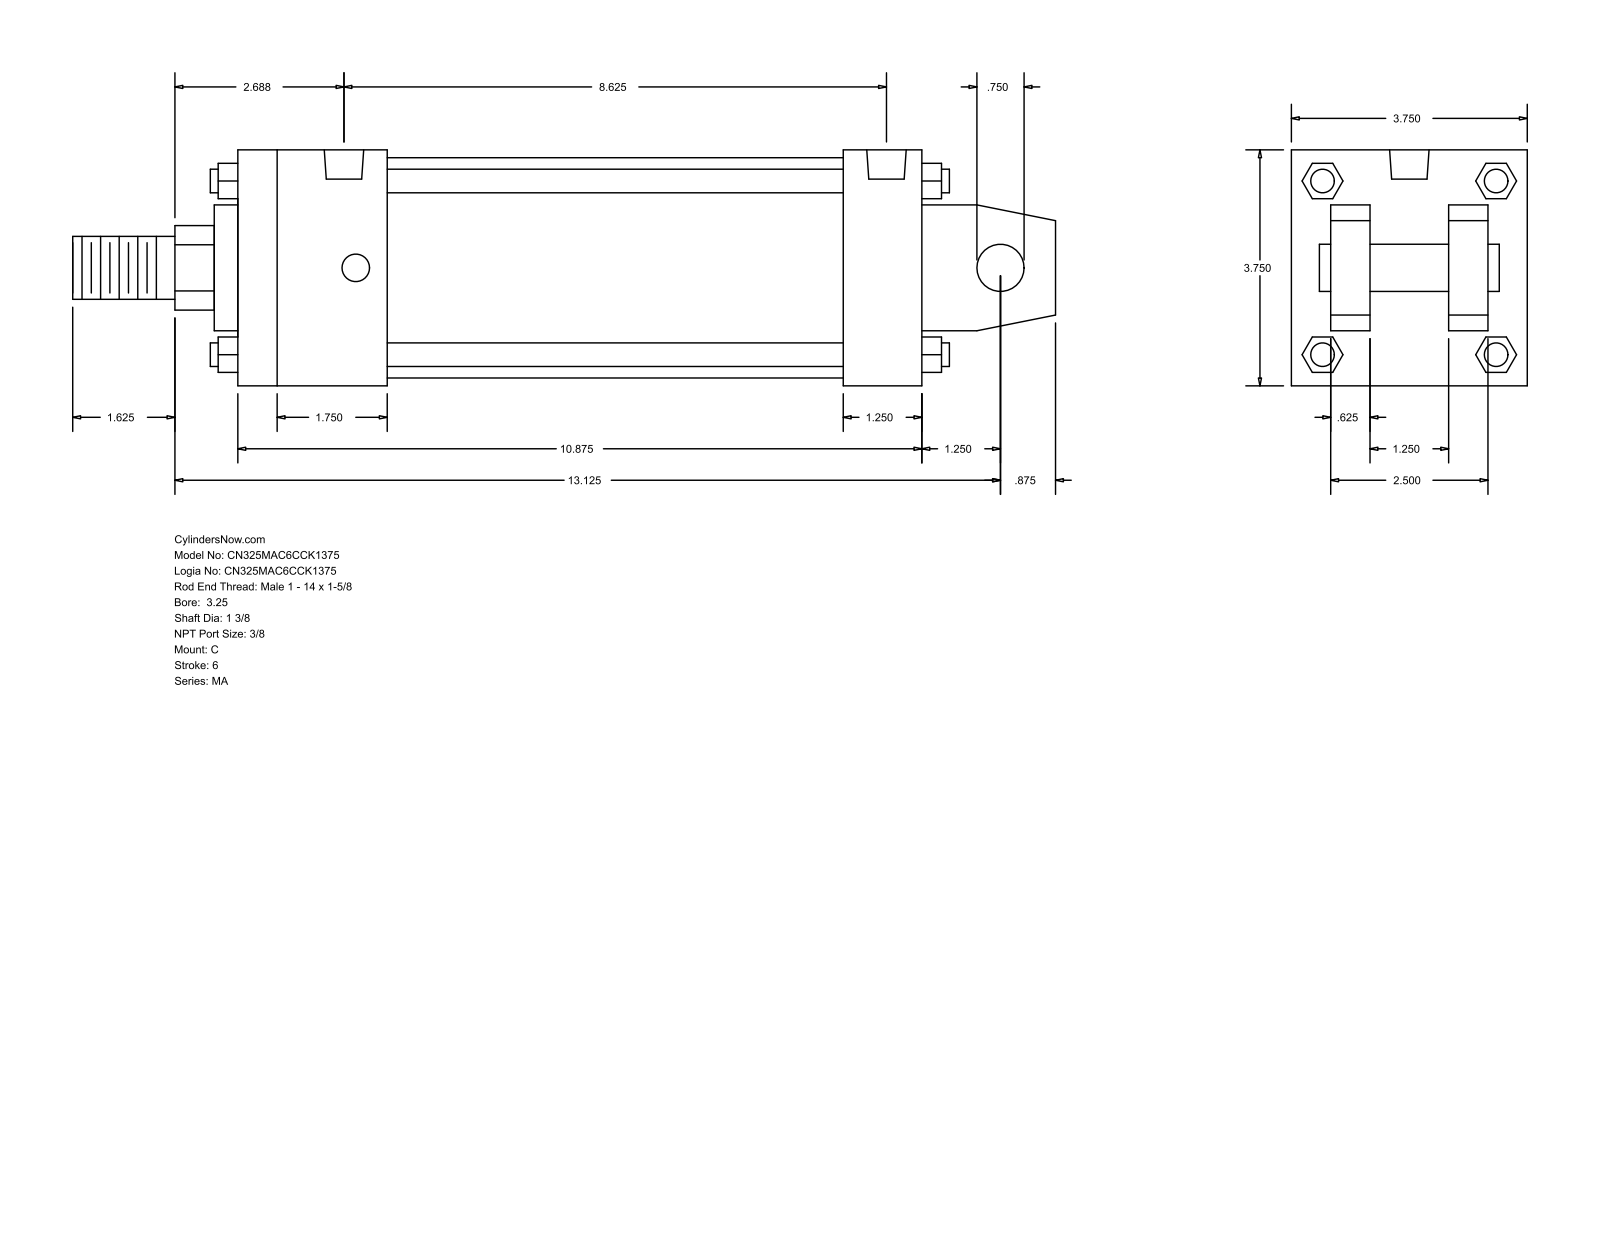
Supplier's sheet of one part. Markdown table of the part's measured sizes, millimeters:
| quantity | value |
| --- | --- |
| part name | MA_C__0325_1.375 |
| STEP written by | GSSL Pune (CONFIG_CONTROL_DESIGN) |
| units | millimeters |
| bodies | 0 solids, 139 faces (108 planar, 31 cylindrical, 0 other) |
| overall size | 396.88 × 95.25 × 95.25 |
| round holes (diameter × count) | 11.11 × 4, 15.93 × 2 |
| round bosses / shafts (diameter × count) | 9.53 × 4, 88.9 × 1, 50.8 × 1, 34.92 × 1, 25.4 × 1, 19.05 × 1 |
| partial cylindrical surfaces (radius × count) | 17.06 × 1 |
| main face-to-face distances | 95.24, 15.87, 31.74, 63.5, 276.22, 79.37, 47.63, 244.48, 60.32, 184.16 |
| hole center spacings | 4.77, 209.54, 214.31, 219.08 |
